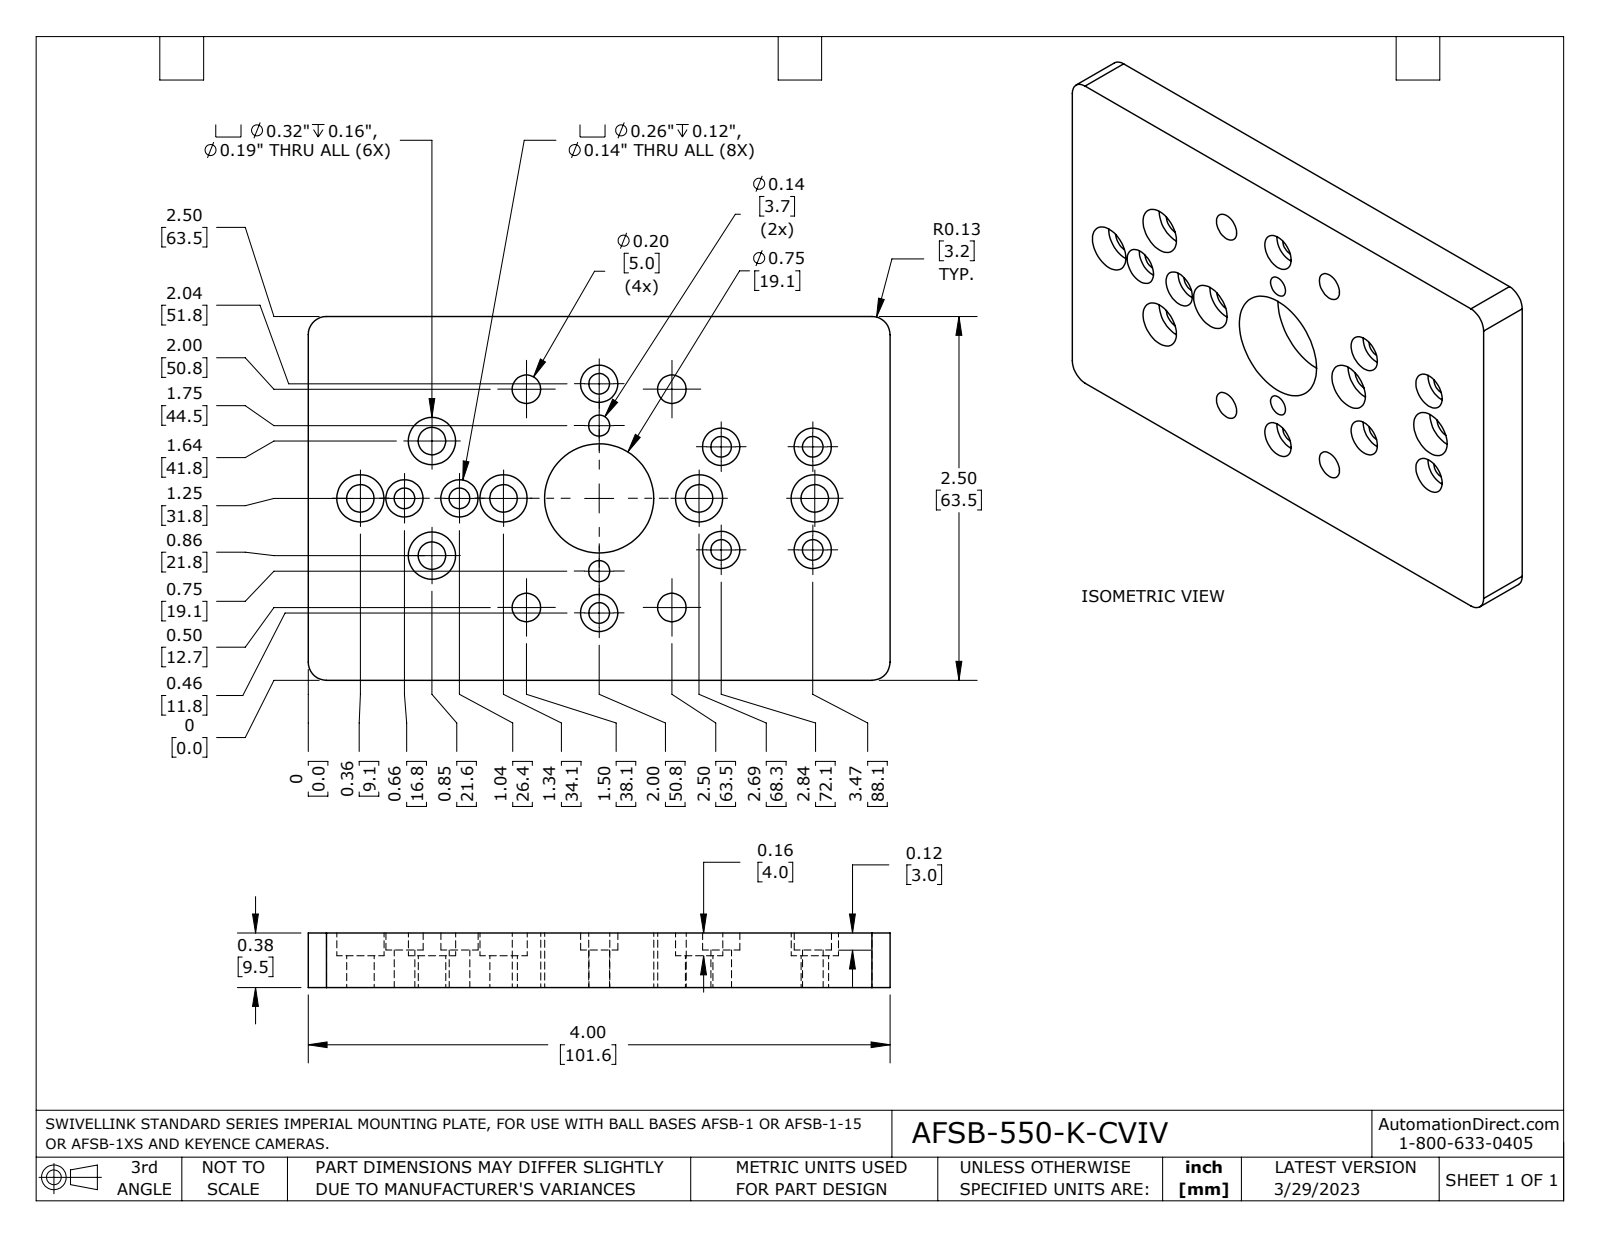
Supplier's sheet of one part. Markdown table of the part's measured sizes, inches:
| quantity | value |
| --- | --- |
| part name | AFSB-550-K-CVIV |
| STEP written by | SolidWorks 2021 (AUTOMOTIVE_DESIGN) |
| units | inches |
| bodies | 1 solid, 59 faces (20 planar, 39 cylindrical, 0 other) |
| overall size | 4 × 2.5 × 0.375 |
| volume | 3.326 in³ |
| surface area | 28.55 in² |
| round holes (diameter × count) | 0.142 × 8, 0.256 × 8, 0.189 × 6, 0.325 × 6, 0.196 × 4, 0.145 × 2, 0.75 × 1 |
| partial cylindrical surfaces (radius × count) | 0.125 × 4 |
| main face-to-face distances | 0.375, 2.5, 4, 0.157, 0.218, 0.118, 0.039, 0.257 |
| hole center spacings | 0.63, 1.215, 1.617, 0.787, 1.642, 0.287, 0.355, 0.385 |
